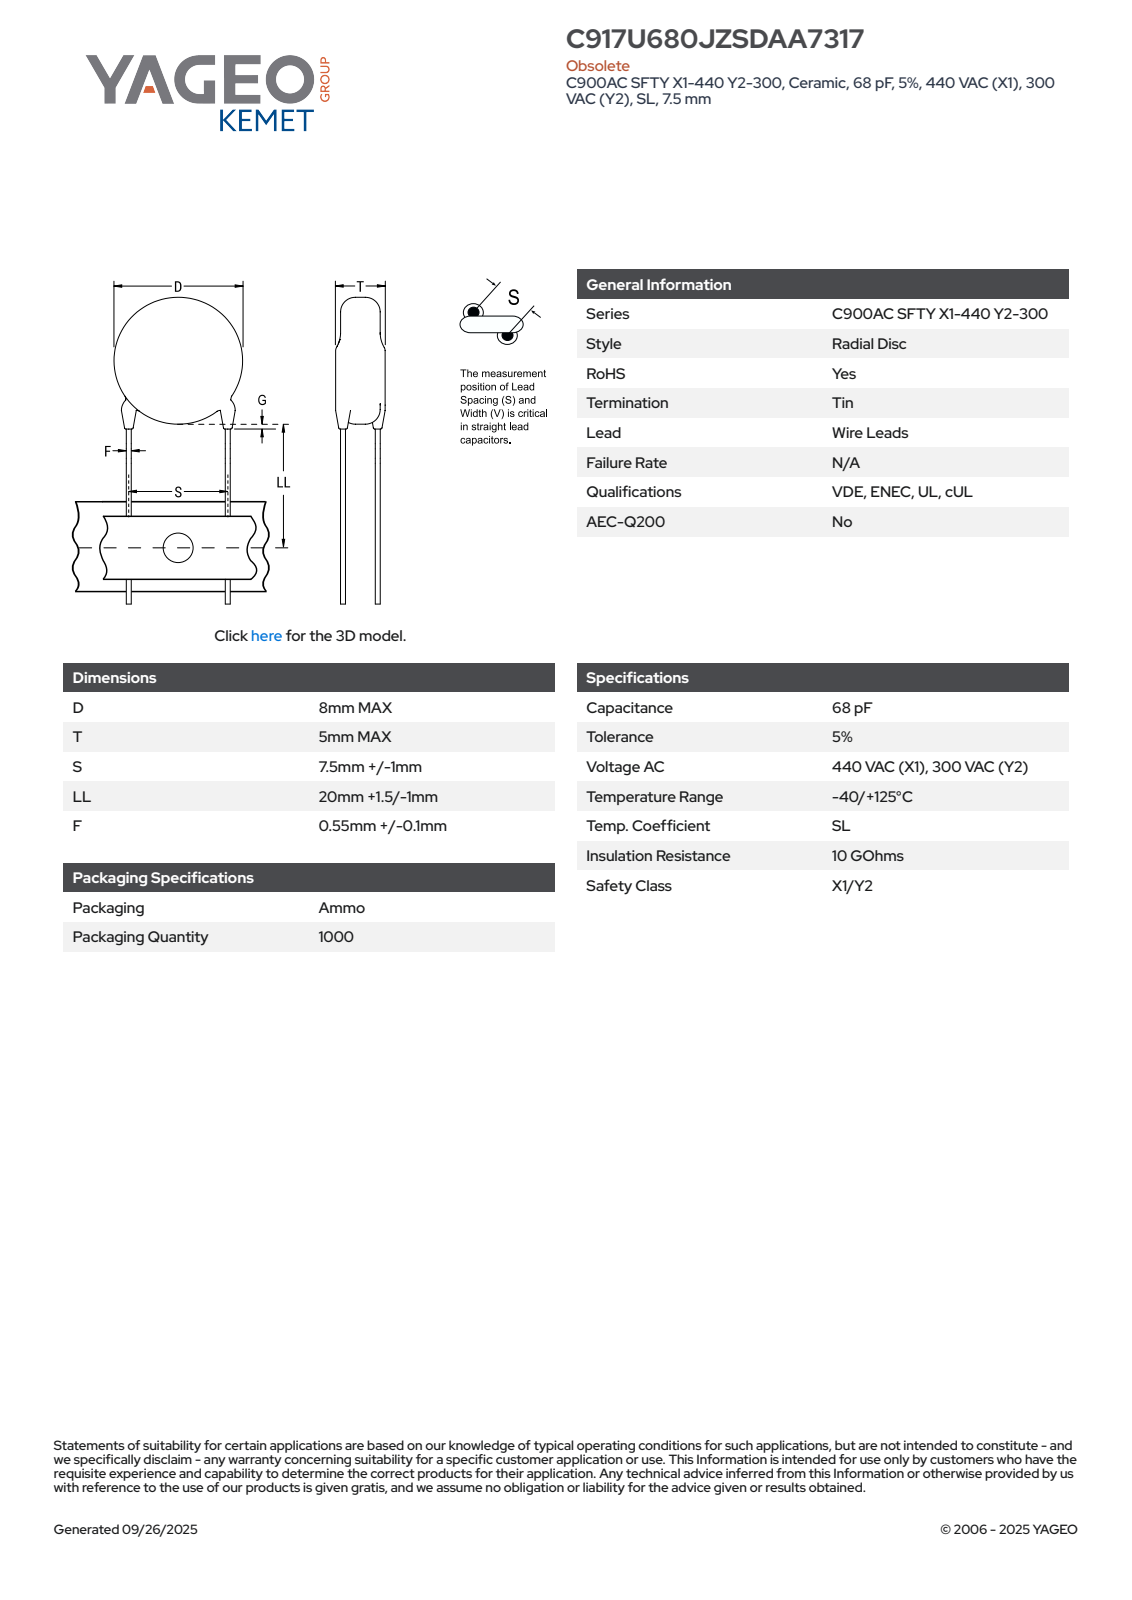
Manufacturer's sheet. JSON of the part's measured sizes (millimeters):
{"part_name": "CCD_STC900_D8T5S7.5LL21.5F0.65G3", "step_written_by": "SolidWorks 2014 (AUTOMOTIVE_DESIGN)", "units": "millimeters", "bodies": {"solids": 4, "faces": 83, "planar": 61, "cylindrical": 6, "other": 16}, "overall_size": [29.5, 8, 5], "volume_mm3": 257, "surface_area_mm2": 304, "round_bosses_or_shafts": [[0.65, 2], [8, 1]], "face_to_face_distances": [5, 25.96, 25.04, 0.92, 0.4, 1.04, 3.77, 0.57, 2.73, 2.84]}
